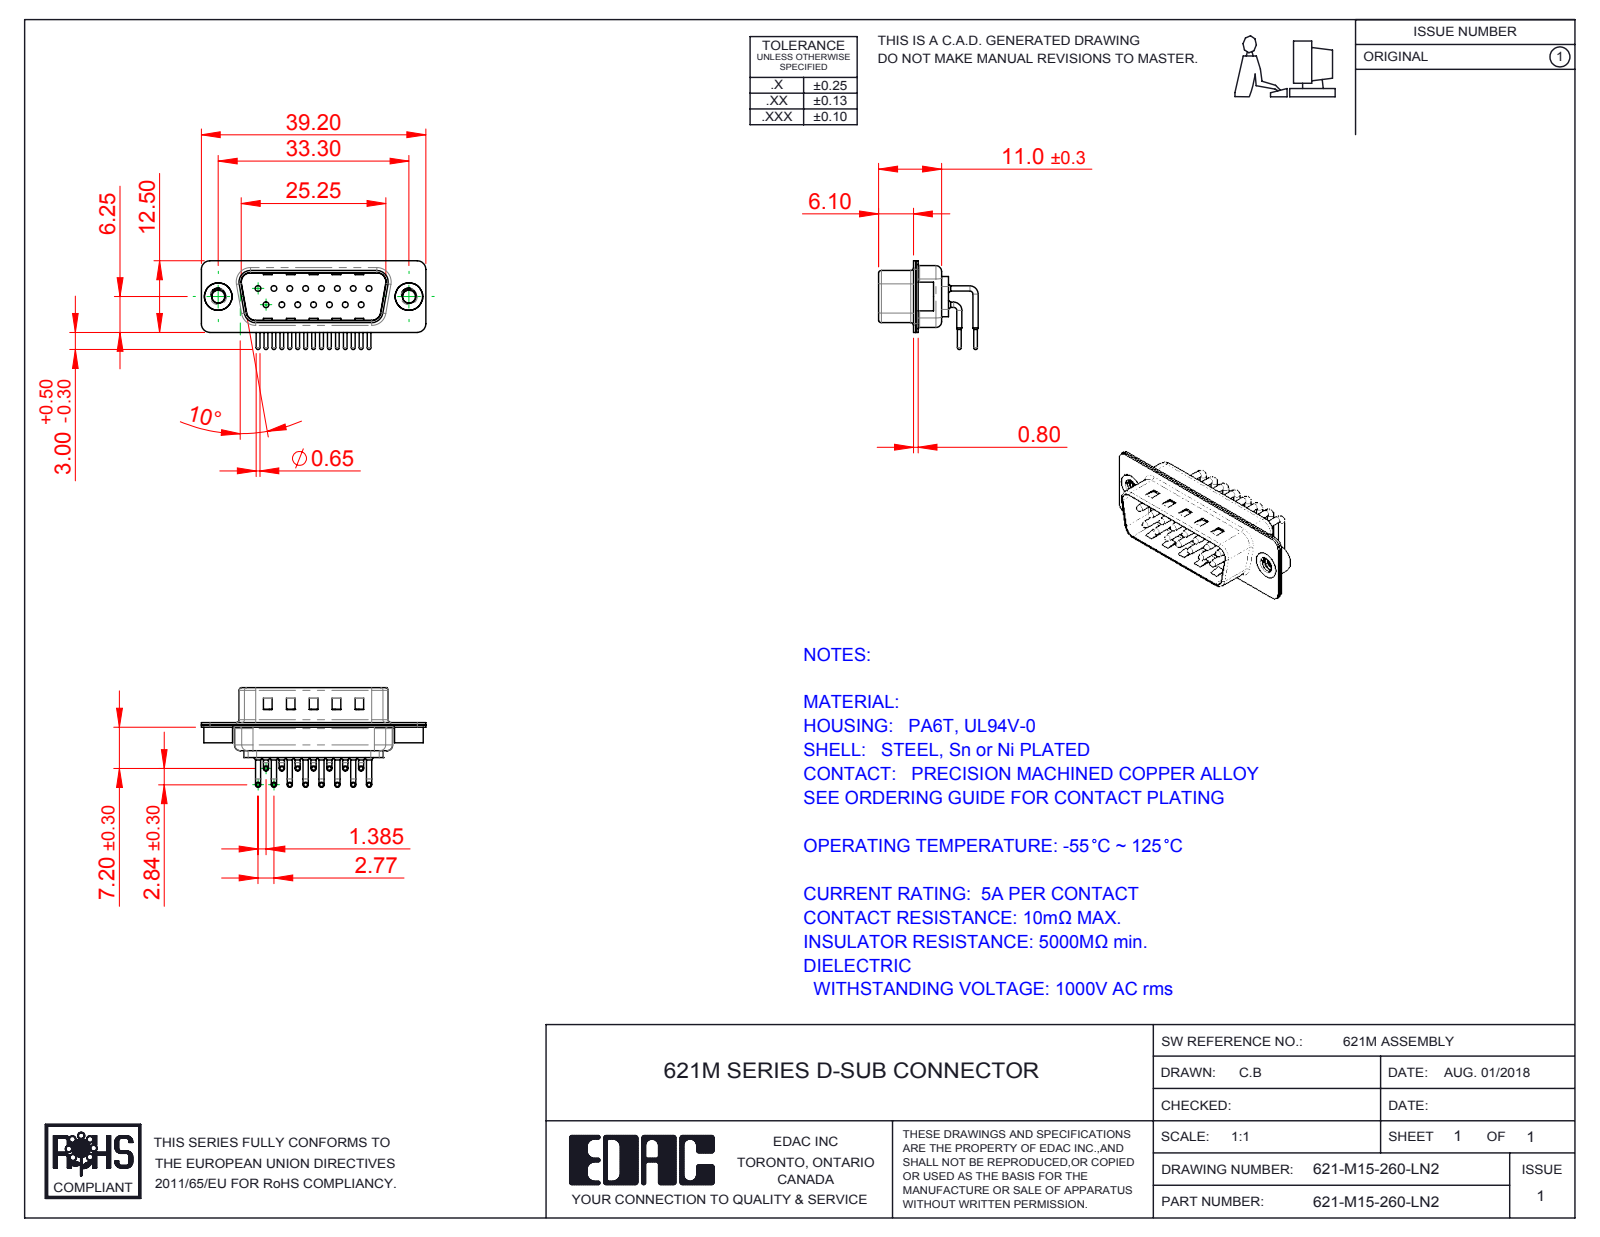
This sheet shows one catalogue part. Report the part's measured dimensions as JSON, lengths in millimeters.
{"part_name": "621M Shell Front_15 Contacts; 621-M15-260-LN2; 621M Contact Row 1; 621M Shell Rear_15 Contacts (+3 more)", "step_written_by": "SolidWorks 2016 (CONFIG_CONTROL_DESIGN)", "units": "millimeters", "bodies": {"solids": 20, "faces": 1990, "planar": 1099, "cylindrical": 673, "other": 218}, "overall_size": [39.2, 17.39, 15.49], "volume_mm3": 1938, "surface_area_mm2": 5262, "round_holes": [[1, 15], [1.7, 15], [2, 15], [2.26, 2], [4, 2], [4.8, 2]], "round_bosses_or_shafts": [[0.9, 30], [1.5, 15], [0.65, 15], [5, 2], [4.9, 2]], "partial_cylinders_radius": [[1.5, 16], [1.01, 15], [2, 12], [0.5, 8], [1.6, 8], [0.25, 4], [0.6, 4], [0.65, 4]], "face_to_face_distances": [0.4, 0.85, 9.55, 8.7, 1.25, 10.4, 0.8, 1.5, 0.35, 1.9], "hole_center_spacings": [3.16, 2.77, 5.54, 8.31, 11.08, 5.03, 5.04, 7.48]}
